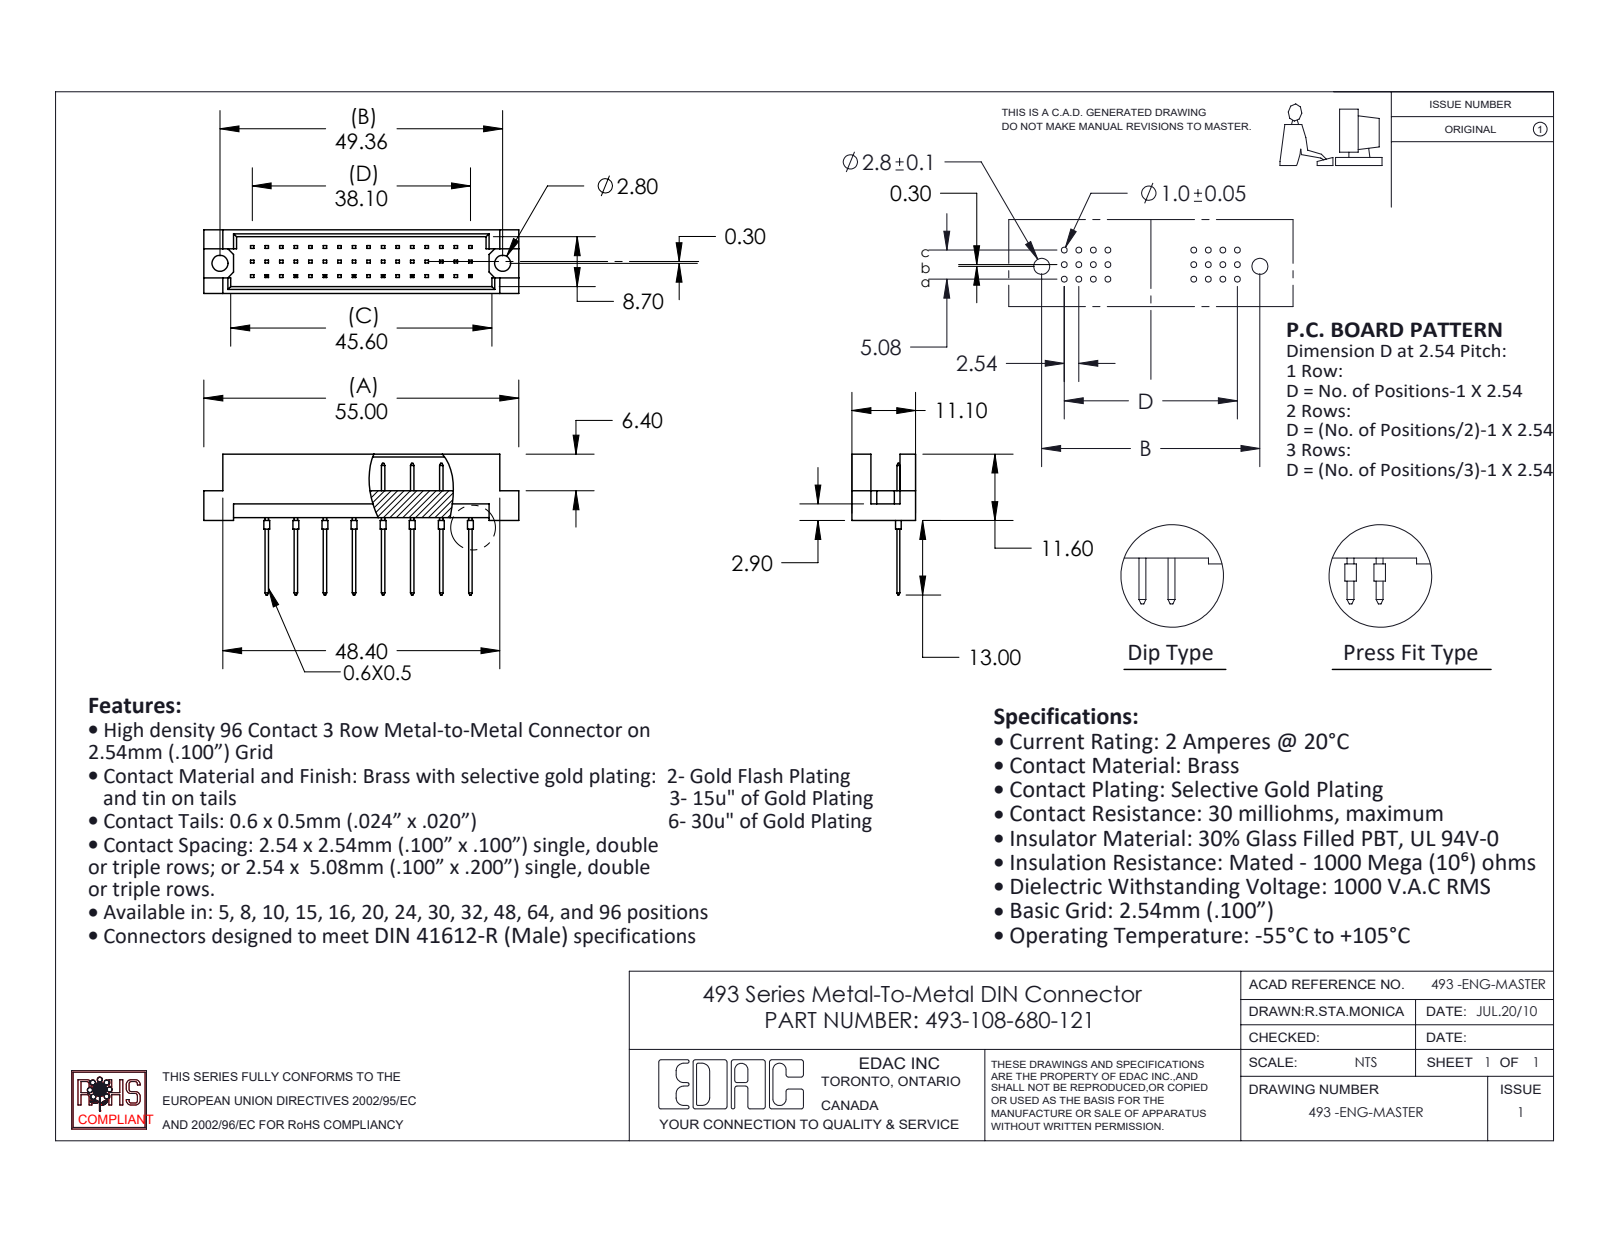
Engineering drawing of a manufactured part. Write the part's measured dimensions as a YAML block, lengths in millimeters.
part_name: "493 Part_48; 493-108-680-122; 493-290_80"
step_written_by: "SolidWorks 2020 (CONFIG_CONTROL_DESIGN)"
units: millimeters
bodies: {solids: 9, faces: 420, planar: 400, cylindrical: 20, other: 0}
overall_size: [55, 24.6, 11.1]
volume: 3333
surface_area: 4177
round_holes:
  - {diameter: 2.8, count: 2}
round_bosses_or_shafts:
  - {diameter: 1, count: 8}
face_to_face_distances: [1.2, 9.9, 11.1, 8.7, 4.7, 0.5, 5.08, 2.76, 8.34, 1.56]
hole_center_spacings: [49.36]
